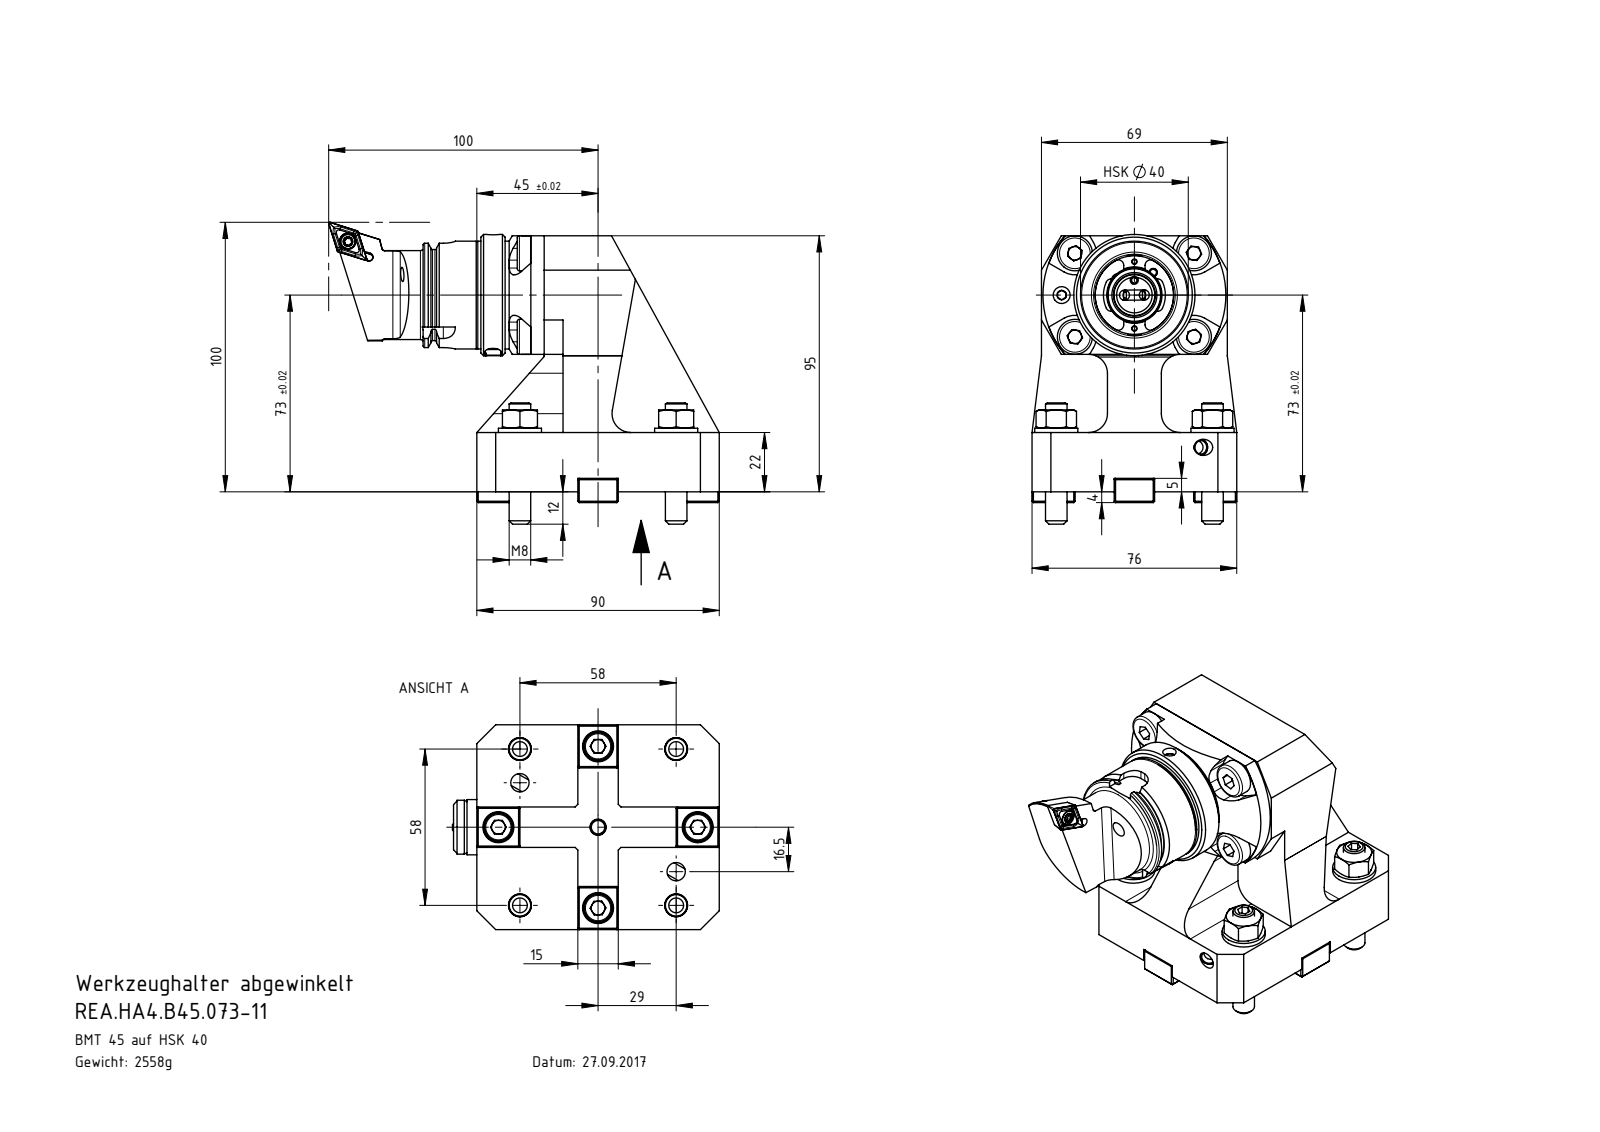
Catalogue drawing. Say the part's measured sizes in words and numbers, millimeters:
The part is named "HA4-ER2.002.005; ISO 4762 - M6 x 8_PreviewCfg; HA4-ER3.003.009; BM5-ER1.015.009_A (+8 more)". Its 3-D file was written by "SolidWorks 2017 (AUTOMOTIVE_DESIGN)". It is 49 solids with 1507 faces: 563 planar, 411 cylindrical and 533 other. Overall it measures 145 by 112 by 76 millimeters. Its volume is 388 489 cubic millimeters and its surface area 110 654 square millimeters. Round holes: 11 of diameter 5, 6 of diameter 6.8, 5 of diameter 11, 4 of diameter 6.5, 4 of diameter 7, 4 of diameter 8.4, 4 of diameter 8.5, 4 of diameter 9, 3 of diameter 4.2, 2 of diameter 1.6, 2 of diameter 3, 2 of diameter 3.5. Round bosses or shafts: 8 of diameter 8, 8 of diameter 6, 5 of diameter 10, 4 of diameter 16, 4 of diameter 13, 1 of diameter 45, 1 of diameter 40, 1 of diameter 39.5. Partial cylindrical surfaces (rounded edges, fillets, slot ends): 9 of radius 5, 8 of radius 1, 6 of radius 0.34, 6 of radius 0.59, 6 of radius 0.9, 5 of radius 7, 4 of radius 1.95, 4 of radius 2. The main face-to-face distances are 17, 5, 22, 48, 20, 28, 90, 25, 42, 45. The hole center spacings are 22.32, 26.99, 29.02, 30.08, 35.59, 41.01, 47.63, 58.
